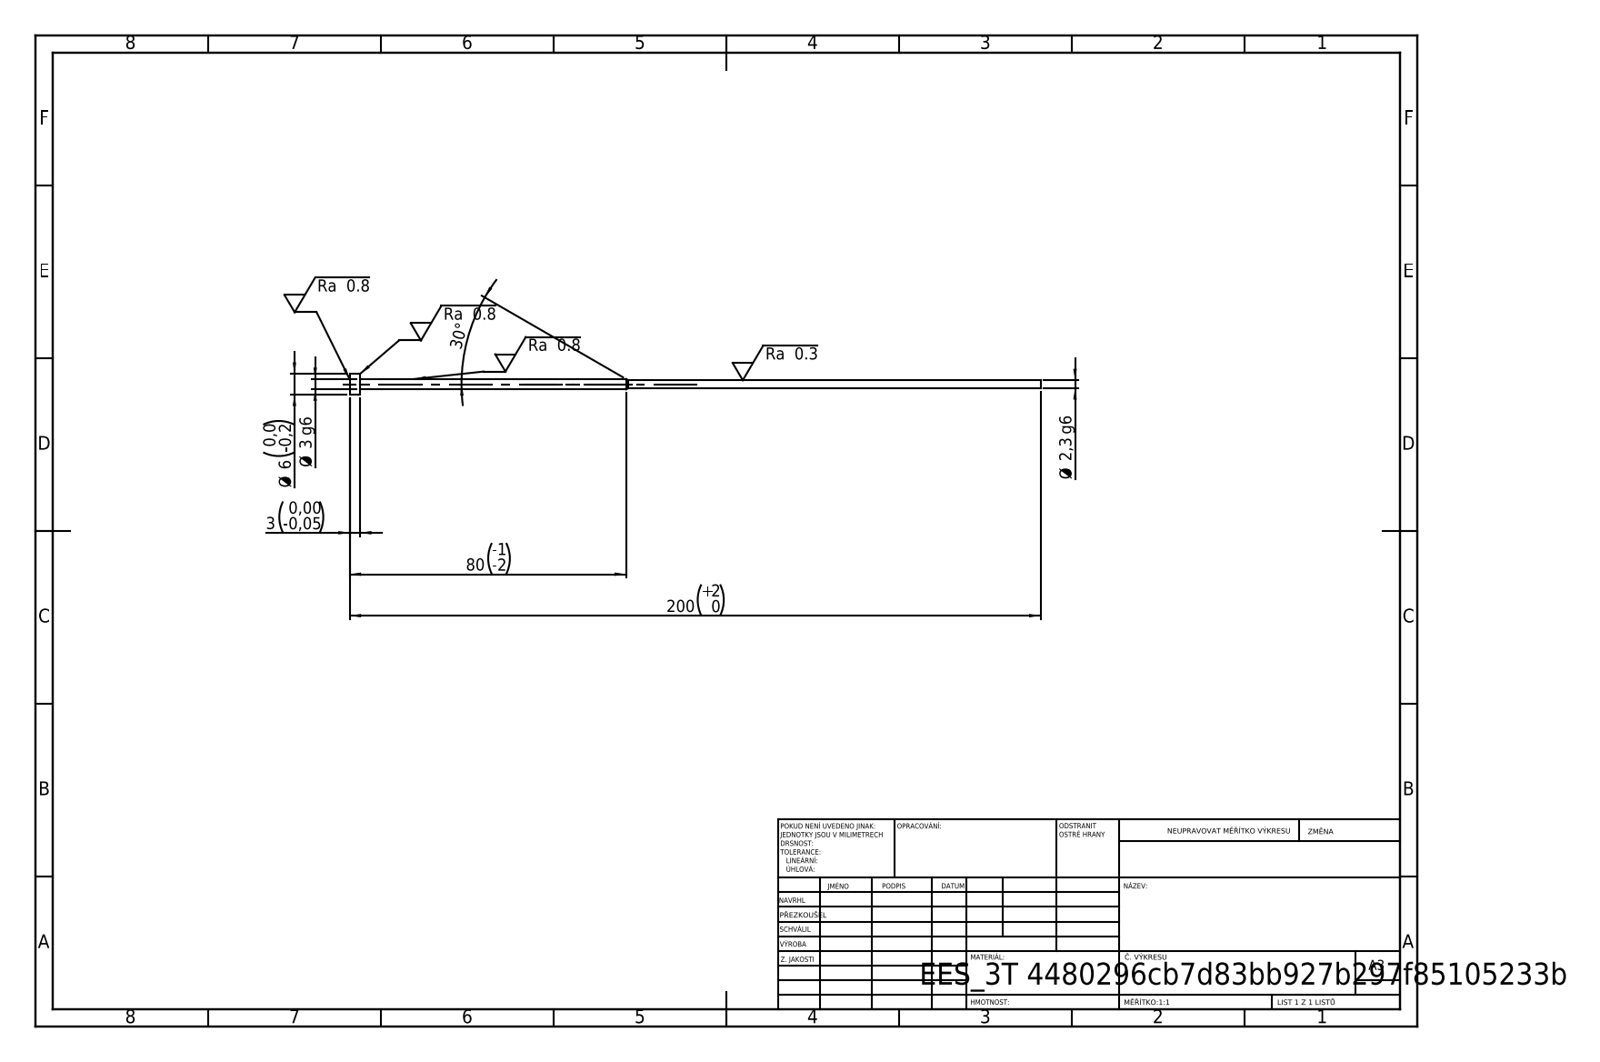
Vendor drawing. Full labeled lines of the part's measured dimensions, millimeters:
STEP written by: SolidWorks 2019 (CONFIG_CONTROL_DESIGN)
Units: millimetres
Bodies: 1 solid, 11 faces (3 planar, 6 cylindrical, 2 other)
Overall size (bounding box): 200 × 6 × 6
Volume: 1 129 mm³ · Surface area: 1 704 mm²
Round bosses / shafts (diameter × count): ⌀6 ×1, ⌀3 ×1, ⌀2.3 ×1
Main face-to-face distances: 3, 197, 200
